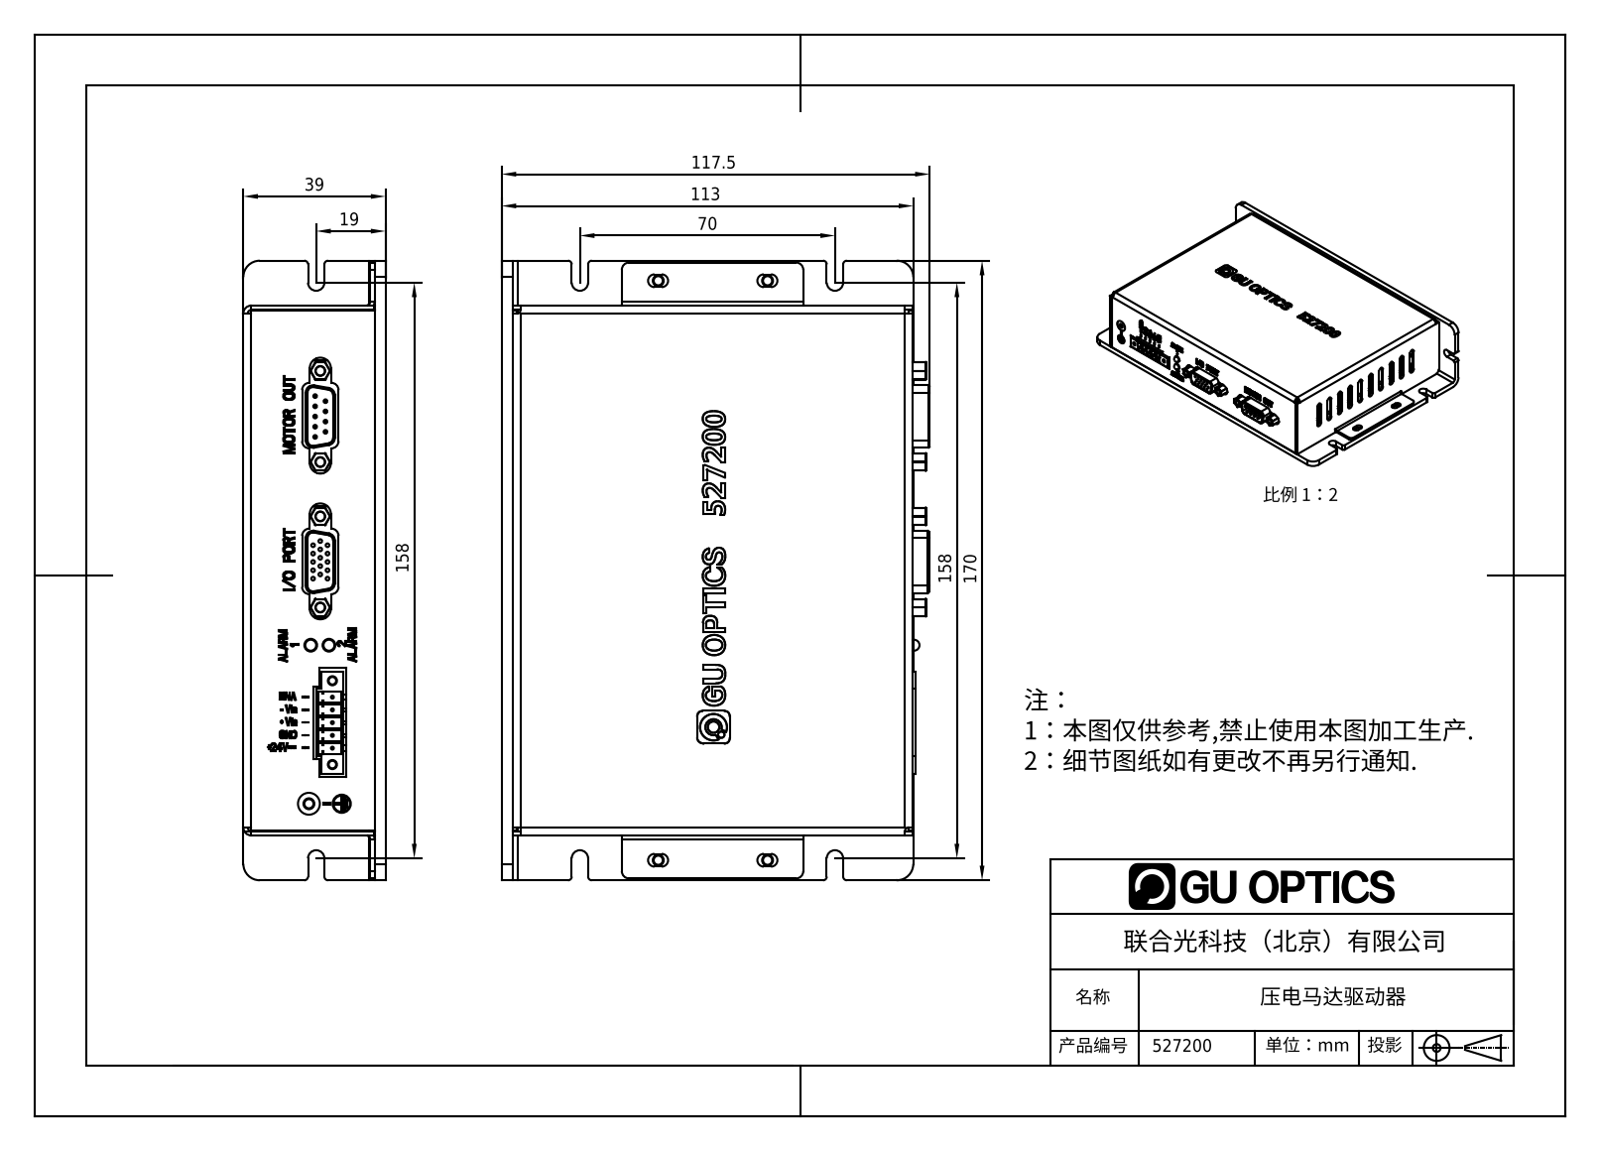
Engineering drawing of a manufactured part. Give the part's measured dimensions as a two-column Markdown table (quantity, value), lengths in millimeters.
| quantity | value |
| --- | --- |
| part name | JIBAN_MINI_DRIVER; YMLZ_M3-8; QUDONG_PCB_MINI; DB-15S (+7 more) |
| STEP written by | CREO PARAMETRIC BY PTC INC, 2014500 (CONFIG_CONTROL_DESIGN) |
| units | millimeters |
| bodies | 17 solids, 2448 faces (1801 planar, 487 cylindrical, 160 other) |
| overall size | 115 × 84.5 × 30.5 |
| volume | 69 044 mm³ |
| surface area | 79 810 mm² |
| round holes (diameter × count) | 2.5 × 15, 1 × 13, 1.2 × 9, 1.5 × 9, 3.5 × 6, 3.8 × 4, 2.05 × 2, 3.2 × 2, 6.2 × 2, 5 × 1, 6 × 1, 10.5 × 1 |
| round bosses / shafts (diameter × count) | 1 × 26, 1.09 × 24, 1.4 × 8, 0.8 × 5, 5.38 × 4, 3 × 4, 4.9 × 3, 5.54 × 2 |
| partial cylindrical surfaces (radius × count) | 1 × 40, 1.5 × 24, 2 × 20, 0.4 × 8, 1.75 × 8, 3 × 7, 2.2 × 6, 2.25 × 6 |
| main face-to-face distances | 1.2, 2.5, 9.6, 7.1, 26.8, 30.5, 28, 20.9, 22.5, 1.6 |
| hole center spacings | 2, 2.83, 4.47, 2.5, 1.95, 3.54, 3.81, 4 |
